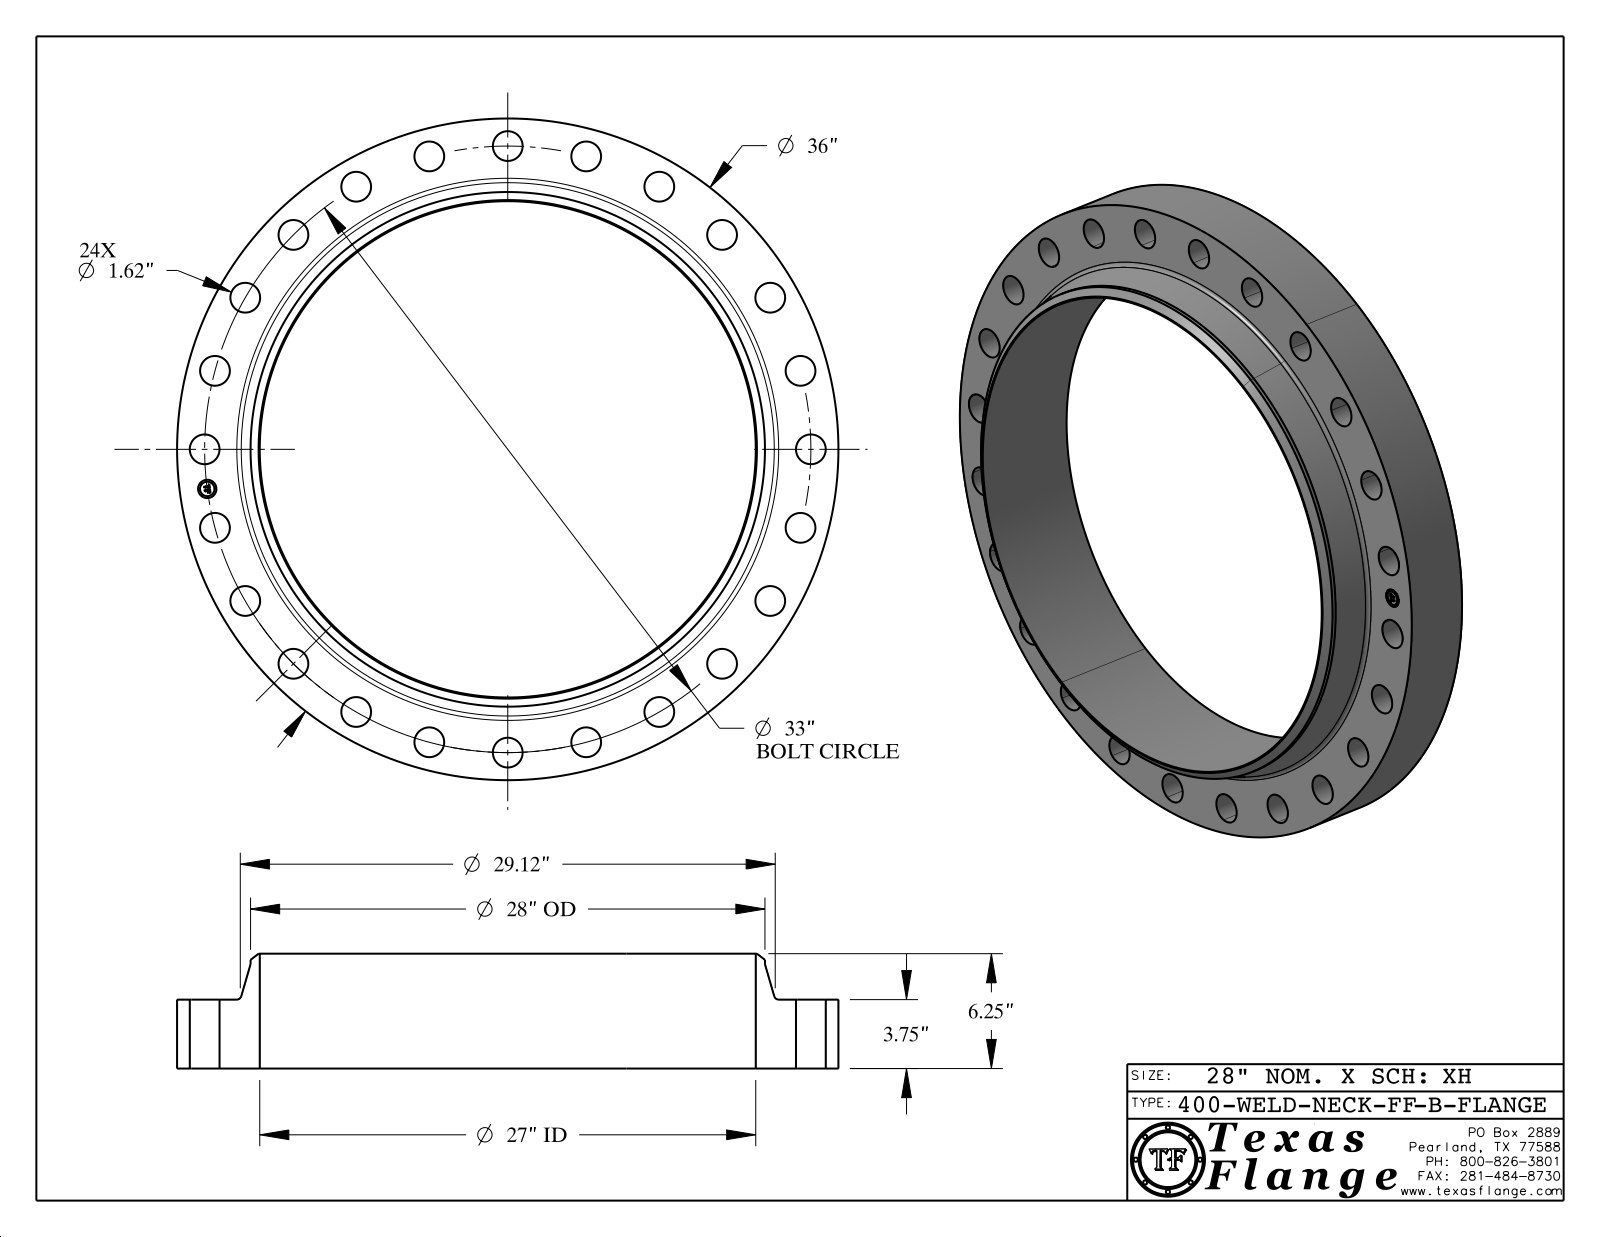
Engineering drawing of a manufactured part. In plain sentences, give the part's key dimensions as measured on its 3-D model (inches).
The part is named "400-WELD-NECK-FF, Series B". Its 3-D file was written by "CATIA V5 STEP AP214 (AUTOMOTIVE_DESIGN)". It is 1 solid with 448 faces: 368 planar, 74 cylindrical and 6 other. Overall it measures 36 by 36 by 6.25 inches. Its volume is 1 635 cubic inches and its surface area 2 360 square inches. Round holes: 24 of diameter 1.62, 1 of diameter 1, 1 of diameter 27. Round bosses or shafts: 8 of diameter 0.061, 1 of diameter 36, 1 of diameter 28, 1 of diameter 0.788. The main face-to-face distances are 3.75, 6.25, 2.5, 3.735, 0.015, 2.515, 0.298, 0.292, 0.054, 0.193. The hole center spacings are 16.5, 4.307, 8.541, 20.089, 23.335, 26.181, 31.876, 32.718.
